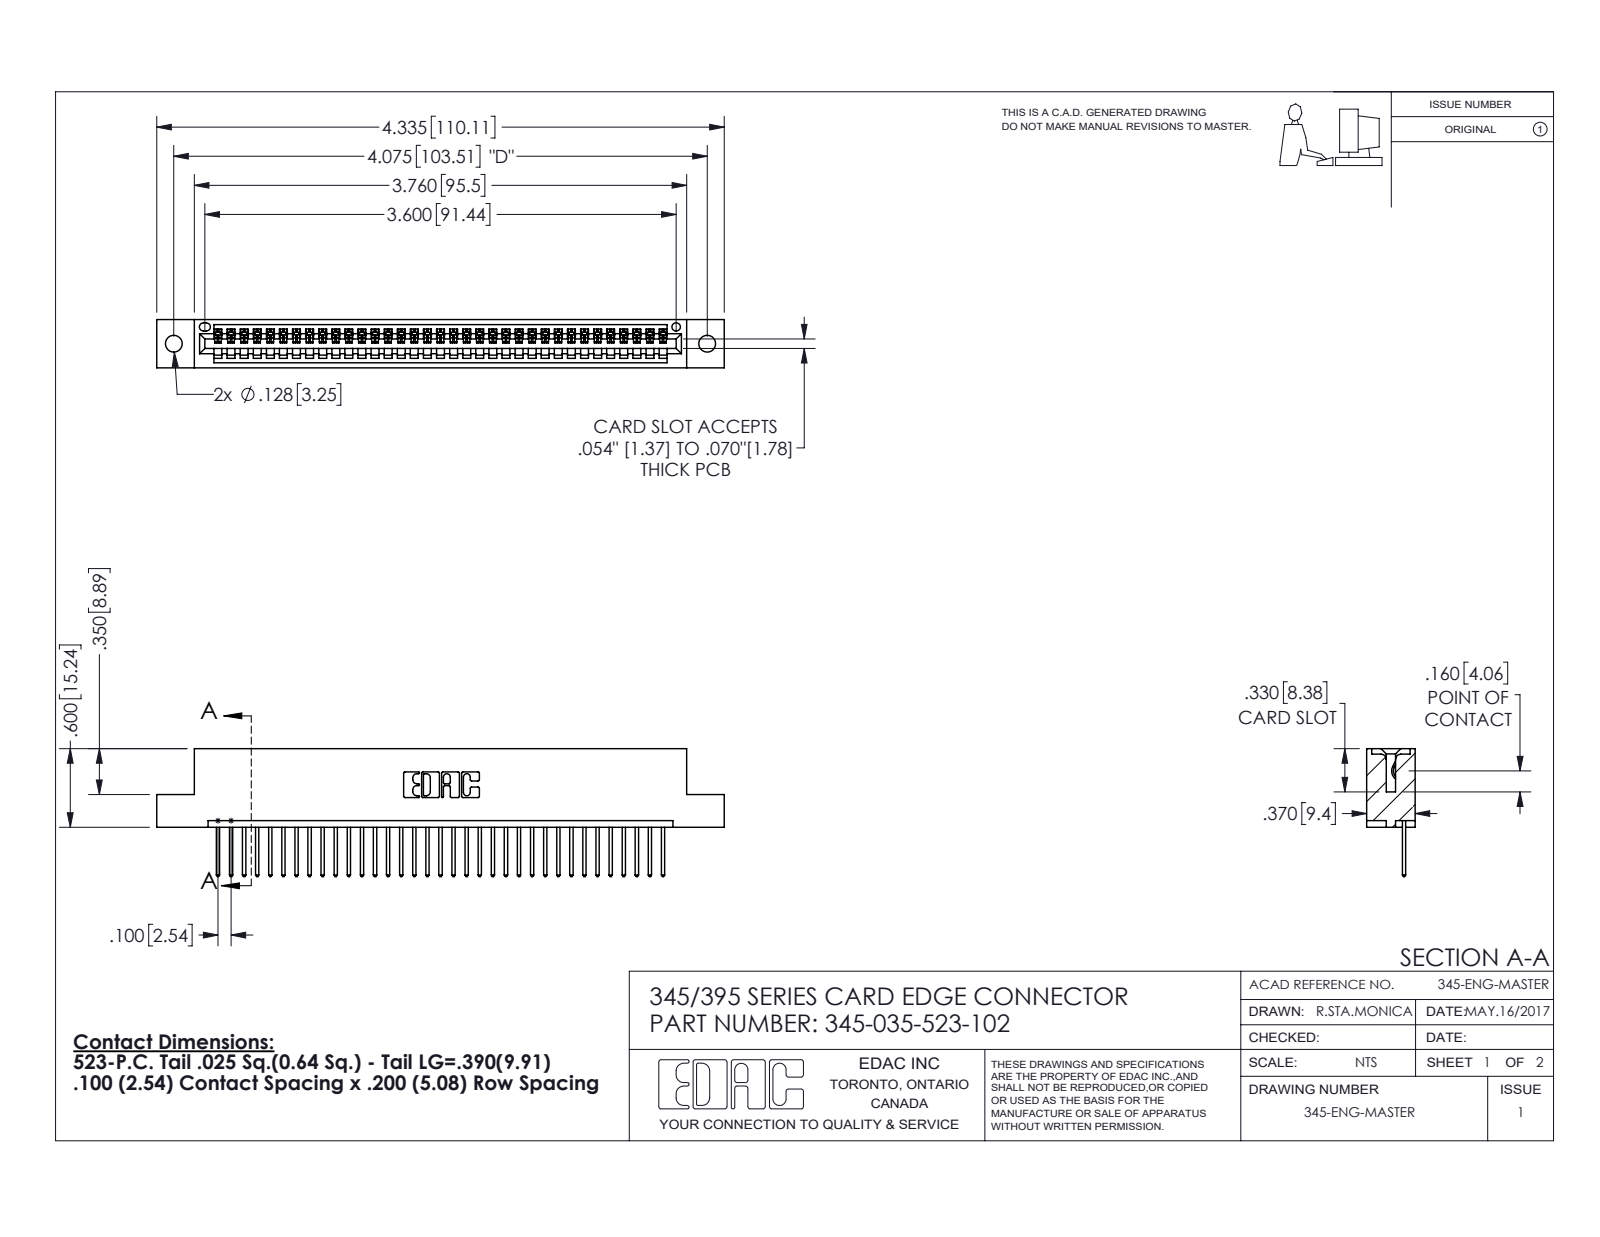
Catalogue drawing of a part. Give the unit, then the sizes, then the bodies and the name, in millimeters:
Units: millimetres
Overall size (bounding box): 110.1 × 24.8 × 9.4
Round holes (diameter × count): ⌀3.3 ×2, ⌀1.6 ×1
Partial cylindrical surfaces — rounded edges, fillets, slot ends (radius × count): R0.2 ×70, R0.3 ×70, R0.3 ×22, R0.2 ×6, R0.8 ×6, R0.7 ×3, R0.8 ×2, R1 ×2
Main face-to-face distances: 7.6, 1.8, 9.4, 5.1, 2.5, 6.9, 0.6, 5.7, 3.8, 1.8
Hole centre spacings: 6.9, 97.5, 103.5
Volume: 10 400 mm³ · Surface area: 13 430 mm²
Bodies: 36 solids, 2156 faces (1480 planar, 676 cylindrical, 0 other)
Part name (STEP PRODUCT): 345-292-001_345-293-123; 345-035-523-102; 345 Part_Flush Mounting Lugs - 0.128 Dia
STEP written by: SolidWorks 2016 (CONFIG_CONTROL_DESIGN)
